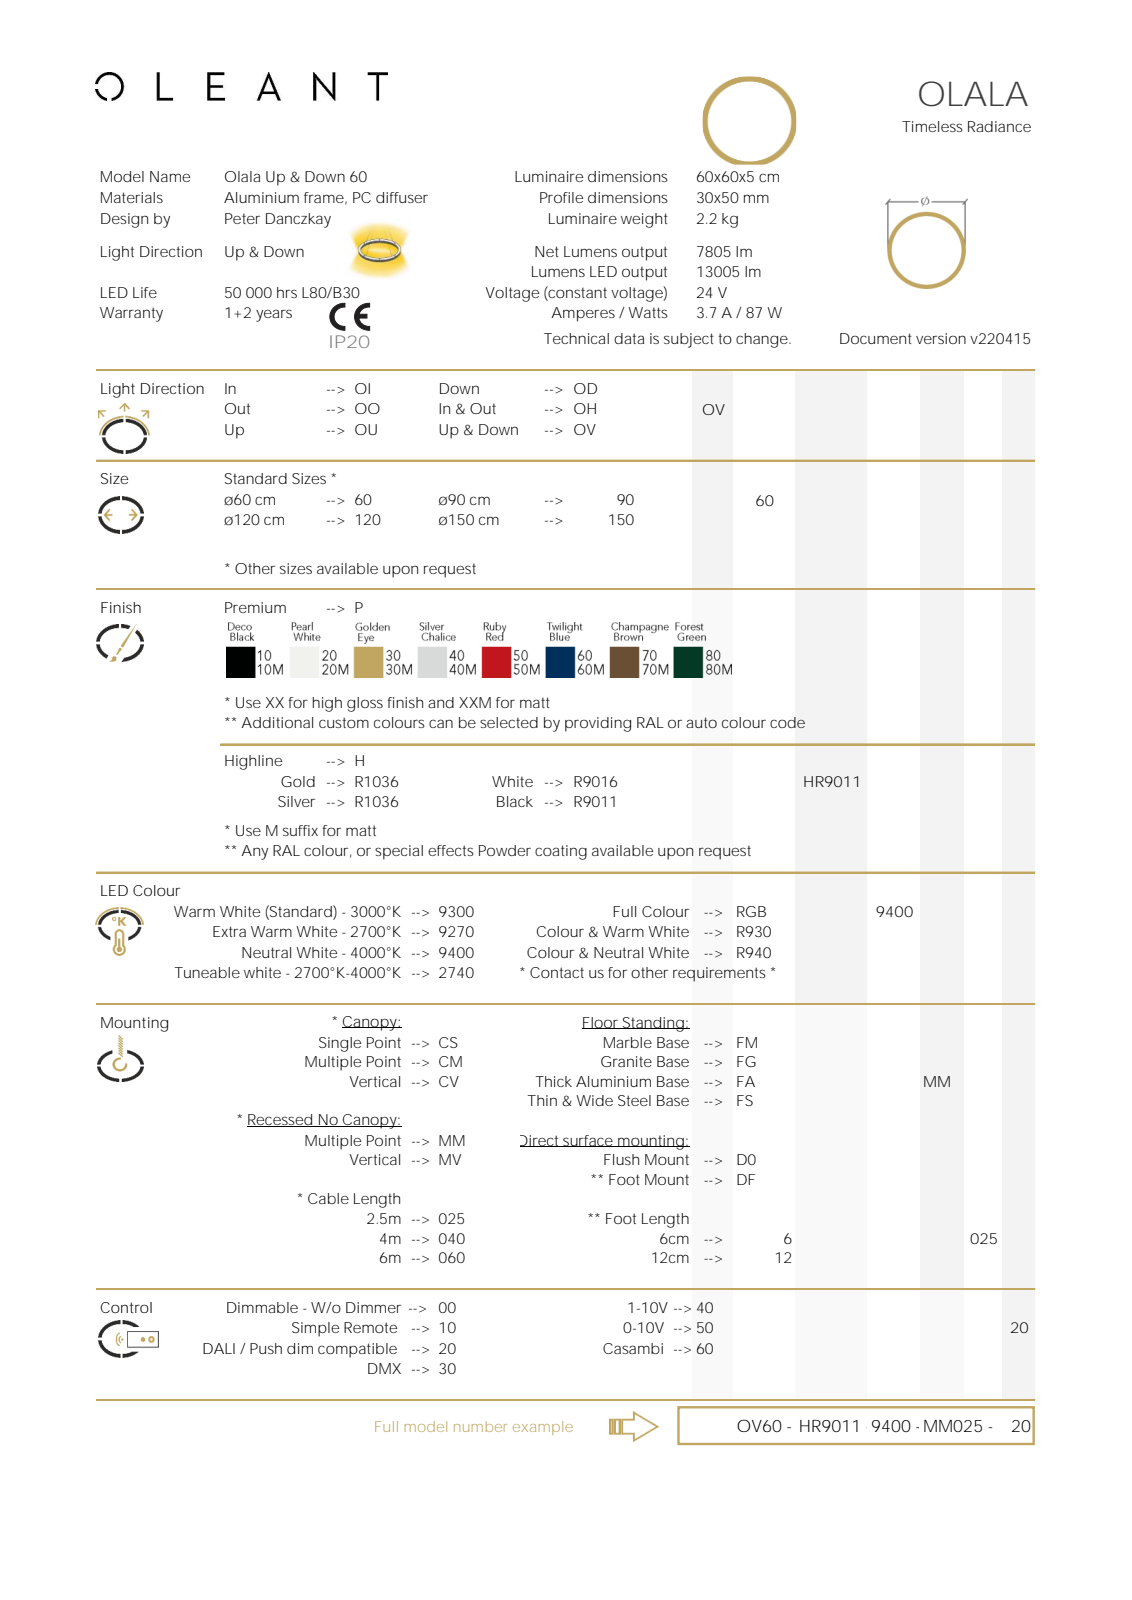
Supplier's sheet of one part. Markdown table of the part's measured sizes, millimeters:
| quantity | value |
| --- | --- |
| part name | olala; frame; plexi; cable (+1 more) |
| STEP written by | Autodesk Inventor 2020 (AUTOMOTIVE_DESIGN) |
| units | millimeters |
| bodies | 8 solids, 78 faces (37 planar, 31 cylindrical, 10 other) |
| overall size | 1073 × 600 × 600 |
| volume | 2 686 000 mm³ |
| surface area | 658 094 mm² |
| round holes (diameter × count) | 3 × 3, 540 × 1, 596 × 1 |
| round bosses / shafts (diameter × count) | 11 × 3, 9 × 3, 4 × 3, 1.2 × 3, 600 × 1, 598 × 1, 544 × 1 |
| main face-to-face distances | 46, 2, 48, 12, 50, 1073, 1071, 1025, 1023, 1052 |
| hole center spacings | 285, 493.64 |
